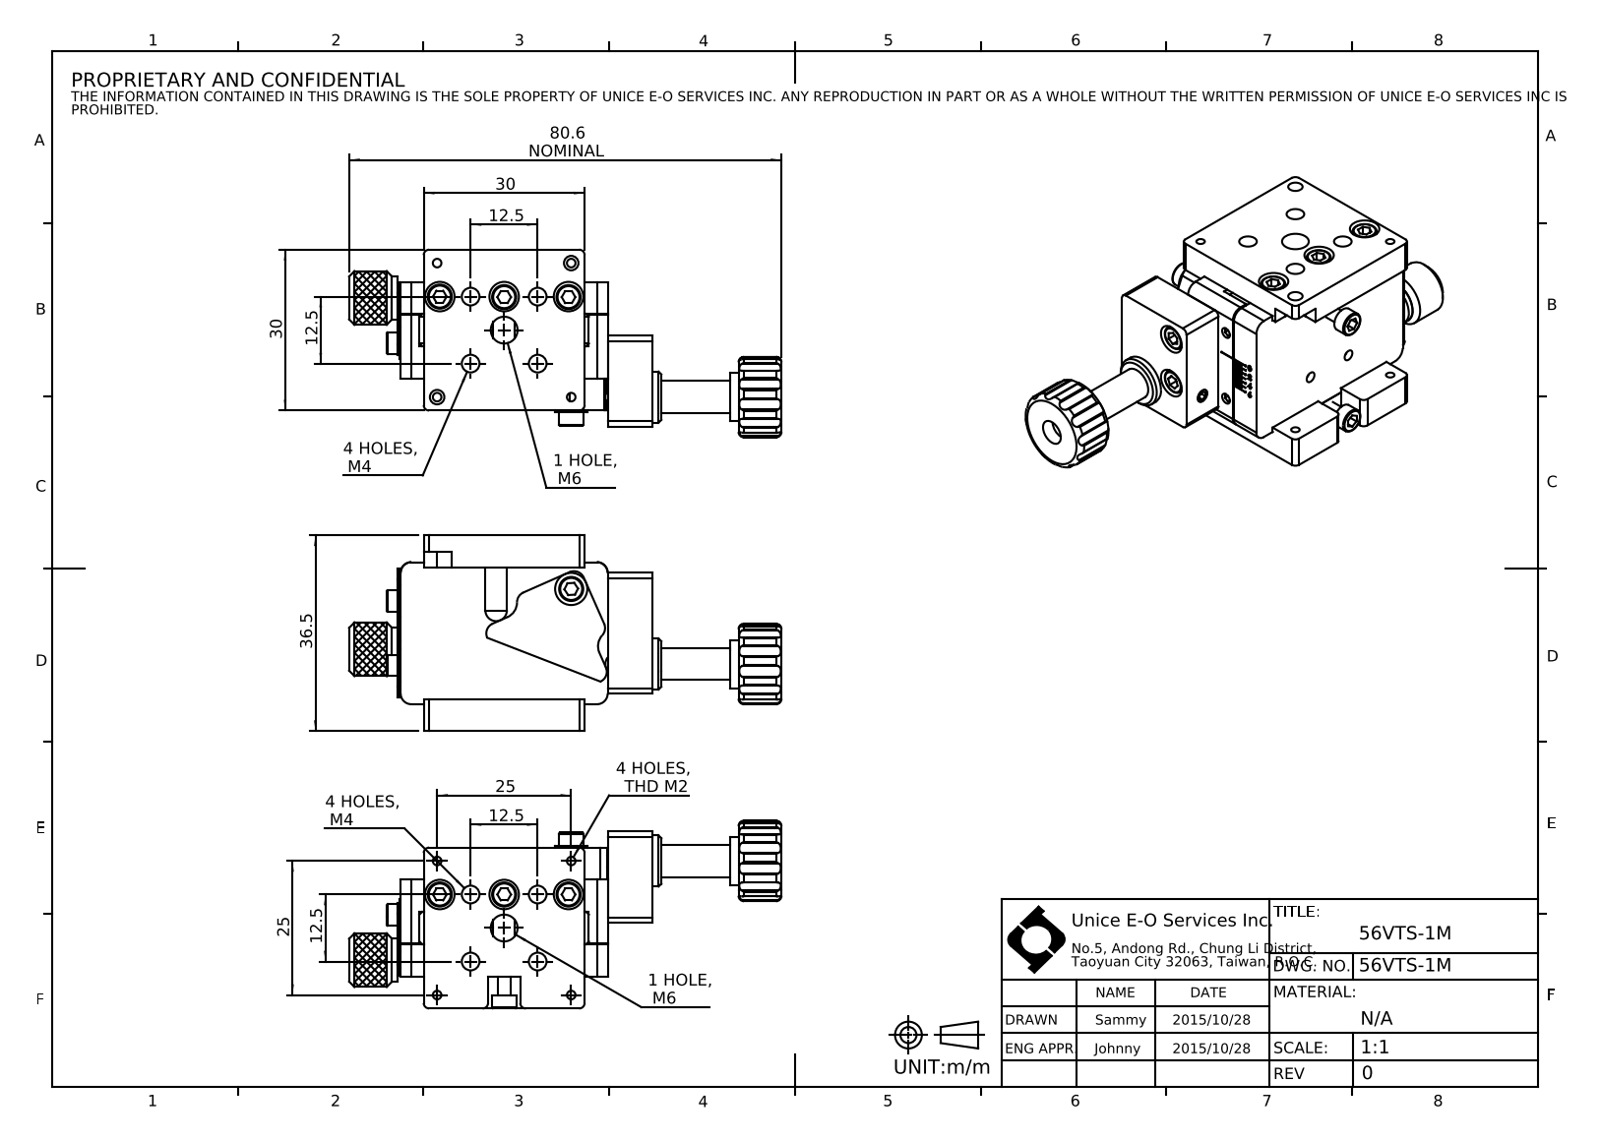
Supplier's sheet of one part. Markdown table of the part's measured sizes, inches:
| quantity | value |
| --- | --- |
| part name | 56VTS-1M |
| STEP written by | SolidWorks 2016 (CONFIG_CONTROL_DESIGN) |
| units | inches |
| bodies | 42 solids, 1038 faces (485 planar, 383 cylindrical, 170 other) |
| overall size | 3.173 × 1.437 × 1.378 |
| volume | 2.011 in³ |
| surface area | 39.77 in² |
| round holes (diameter × count) | 0.081 × 22, 0.118 × 10, 0.197 × 9, 0.114 × 8, 0.217 × 8, 0.063 × 6, 0.098 × 6, 0.008 × 4, 0.13 × 4, 0.126 × 3, 0.087 × 2, 0.106 × 2 |
| round bosses / shafts (diameter × count) | 0.098 × 17, 0.177 × 15, 0.236 × 3, 0.157 × 2, 0.079 × 2, 0.394 × 1, 0.354 × 1, 0.315 × 1 |
| partial cylindrical surfaces (radius × count) | 0.012 × 24, 0.079 × 13, 0.059 × 12, 0.039 × 10, 0.071 × 2, 0.108 × 2, 0.118 × 2, 0.295 × 1 |
| main face-to-face distances | 0.236, 0.472, 0.709, 0.197, 1.24, 0.232, 0.039, 0.476, 0.24, 0.469 |
| hole center spacings | 0.472, 0.492, 0.246, 0.348, 0.55, 0.778, 0.226, 0.547 |
